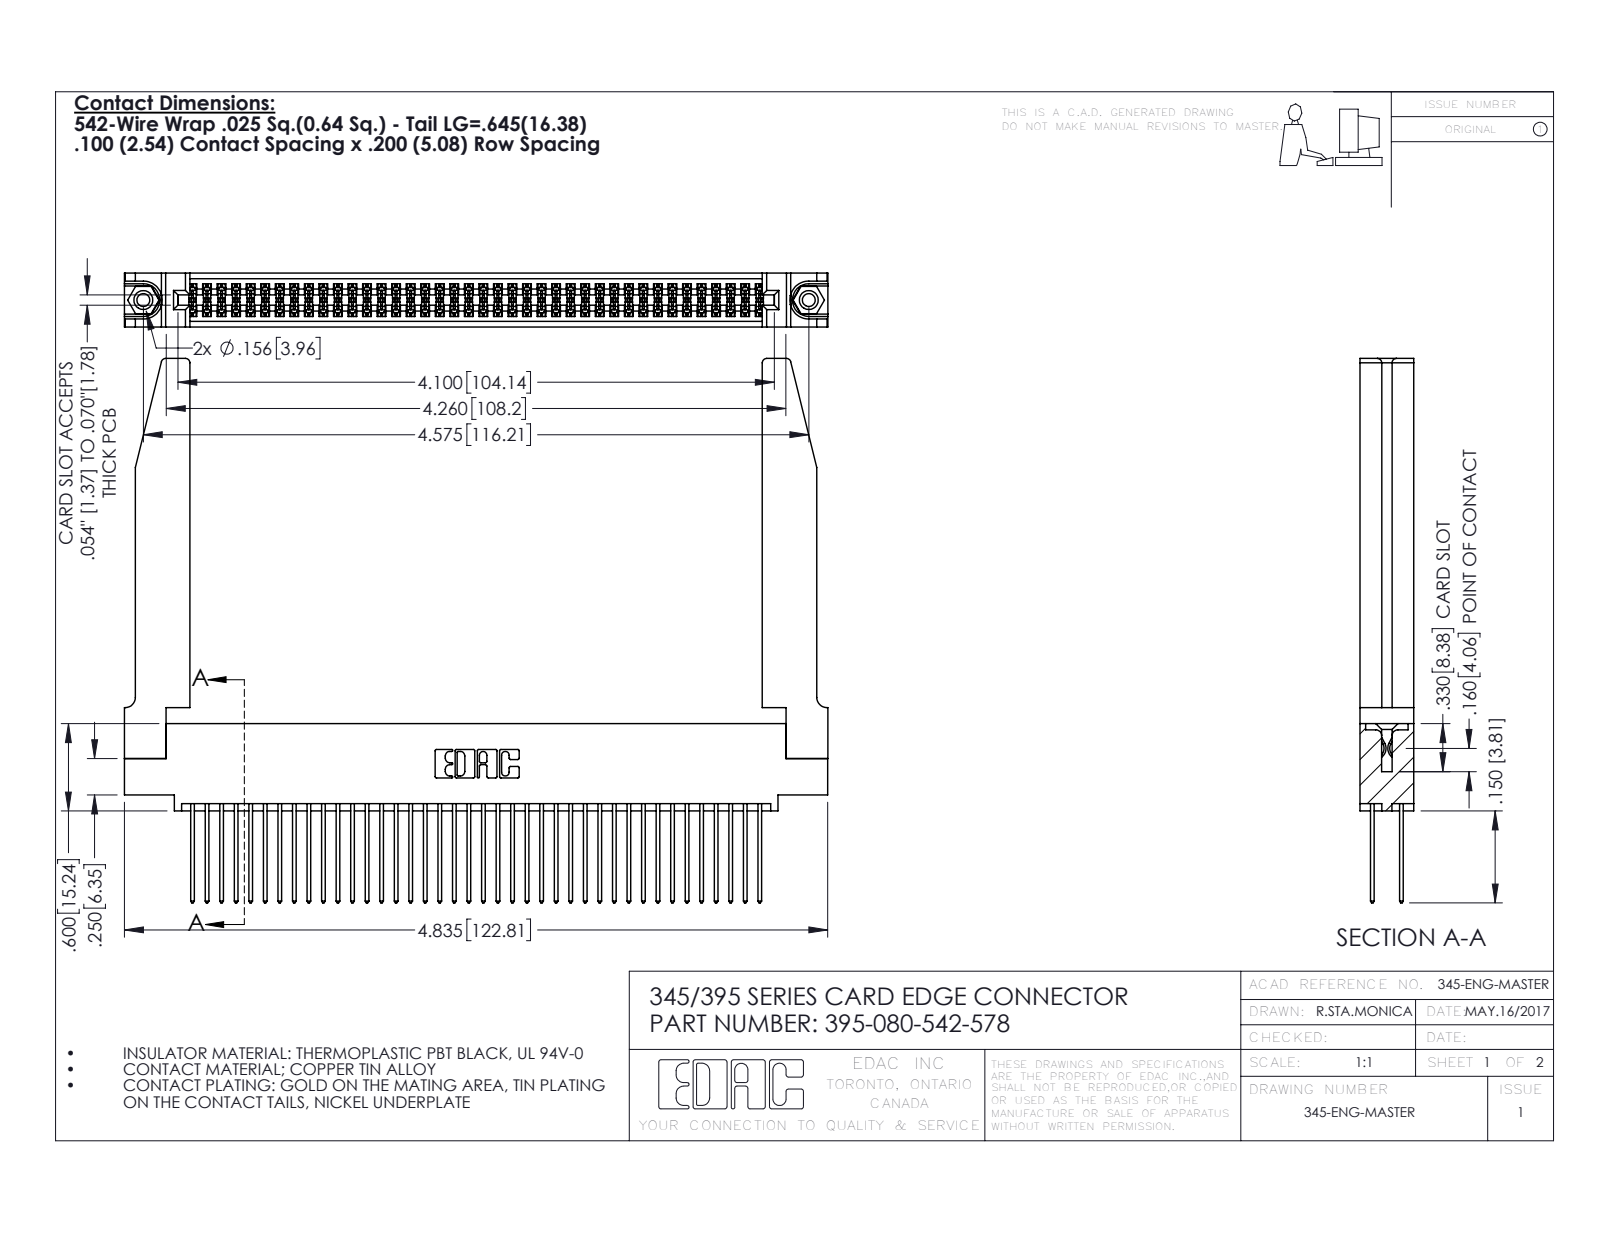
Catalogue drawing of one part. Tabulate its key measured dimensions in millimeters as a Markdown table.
| quantity | value |
| --- | --- |
| part name | 345 Part_0.110 Offset - 0.156 Dia-TH; 345-292-001_345-293-142; 345-220-078_345-220-078; 345-250-001_345-250-001-102 (+1 more) |
| STEP written by | SolidWorks 2016 (CONFIG_CONTROL_DESIGN) |
| units | millimeters |
| bodies | 85 solids, 4364 faces (2866 planar, 1446 cylindrical, 52 other) |
| overall size | 122.8 × 95 × 9.4 |
| volume | 19 980 mm³ |
| surface area | 26 690 mm² |
| round holes (diameter × count) | 2.3 × 2, 3.2 × 2, 4 × 2, 1.6 × 1 |
| round bosses / shafts (diameter × count) | 3.9 × 2 |
| partial cylindrical surfaces (radius × count) | 0.2 × 120, 0.3 × 80, 0.3 × 22, 0.8 × 8, 0.2 × 6, 0.8 × 6, 0.7 × 3, 0.4 × 2 |
| main face-to-face distances | 1.8, 7.6, 9.4, 5.1, 2.5, 6.9, 0.6, 5.7, 4.4, 3.8 |
| hole center spacings | 6.9, 110.2, 116.2 |
